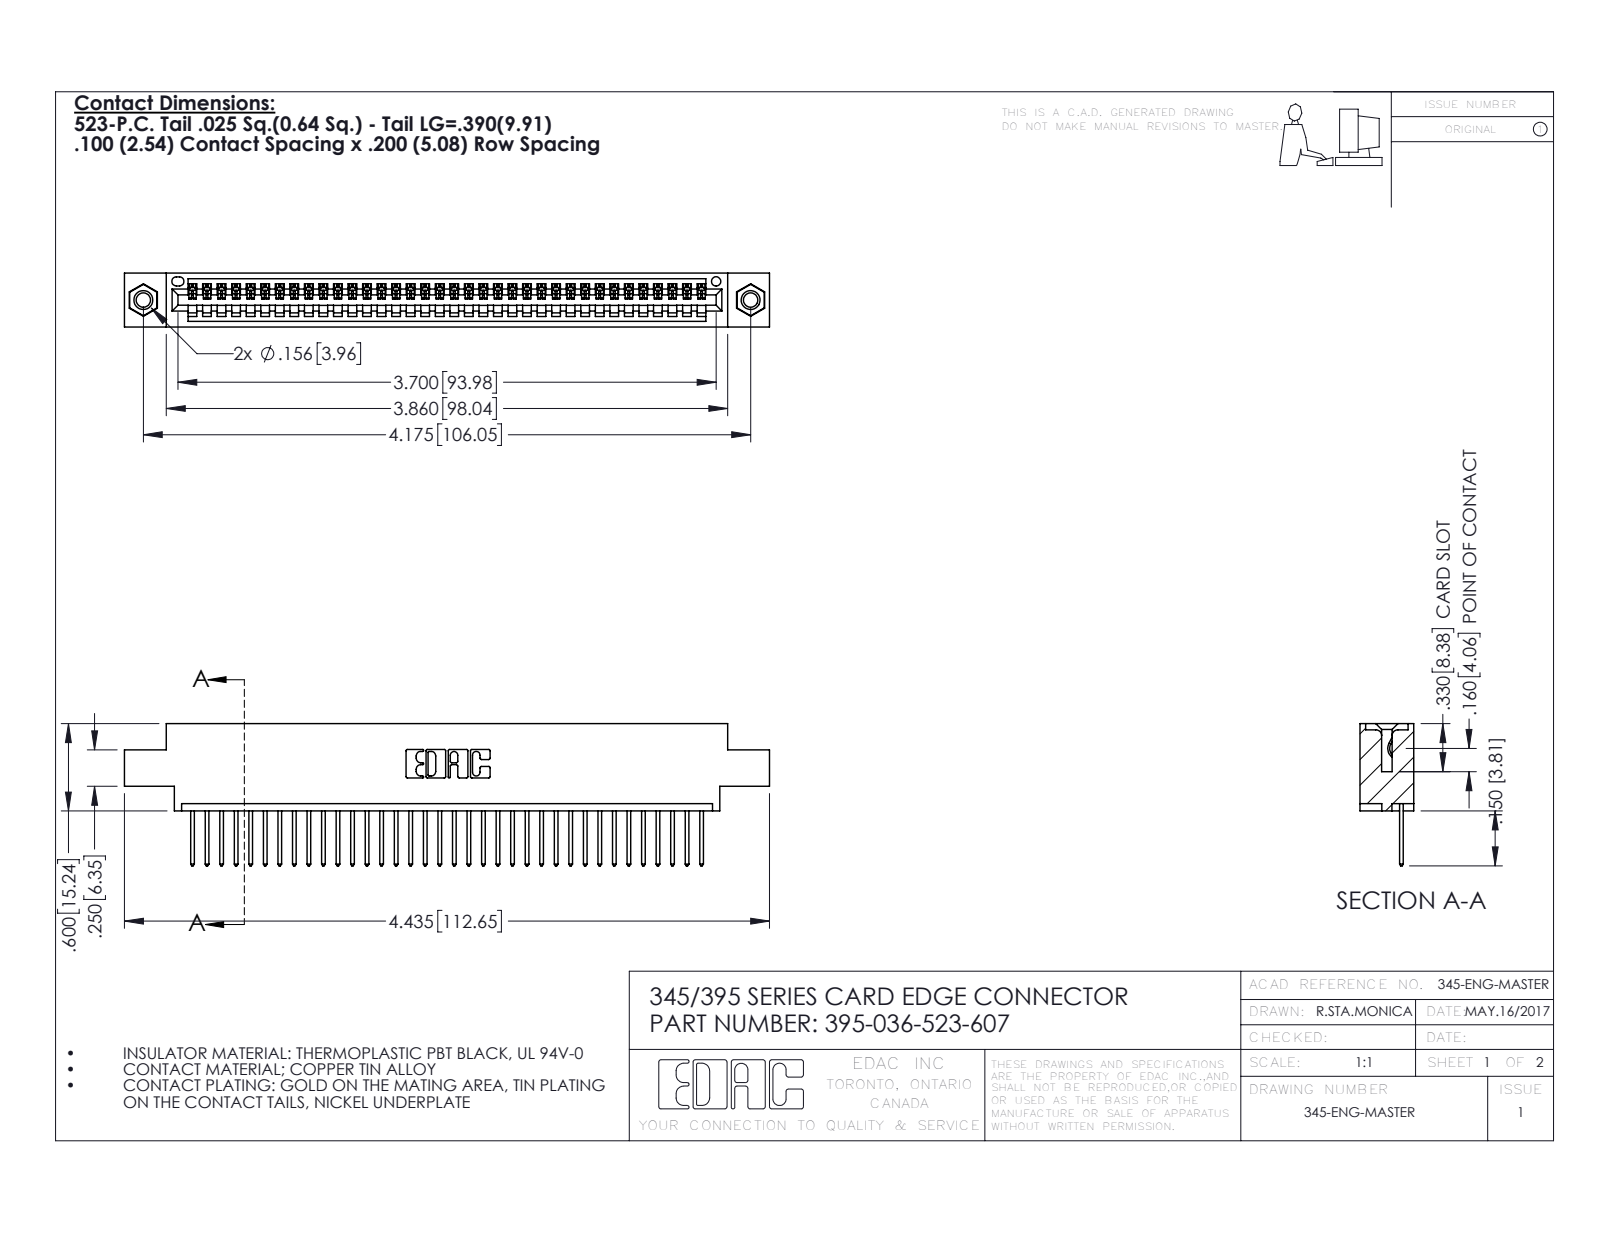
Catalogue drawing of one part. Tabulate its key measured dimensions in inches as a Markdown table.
| quantity | value |
| --- | --- |
| part name | 345-250-001_345-250-005-103; 345 Part_0.170 Offset - 0.156 Dia-TI; 345-292-001_345-293-123; 395-036-523-607 |
| STEP written by | SolidWorks 2016 (CONFIG_CONTROL_DESIGN) |
| units | inches |
| bodies | 39 solids, 2278 faces (1556 planar, 706 cylindrical, 16 other) |
| overall size | 4.435 × 0.977 × 0.37 |
| volume | 0.641 in³ |
| surface area | 21.83 in² |
| round holes (diameter × count) | 0.098 × 2, 0.125 × 2, 0.156 × 2, 0.064 × 1 |
| round bosses / shafts (diameter × count) | 0.155 × 2 |
| partial cylindrical surfaces (radius × count) | 0.006 × 72, 0.01 × 72, 0.01 × 22, 0.007 × 6, 0.031 × 6, 0.026 × 3, 0.031 × 2, 0.04 × 2 |
| main face-to-face distances | 0.072, 0.298, 0.37, 0.2, 0.098, 0.272, 0.025, 0.225, 0.175, 0.149 |
| hole center spacings | 0.27, 3.939, 4.175 |
